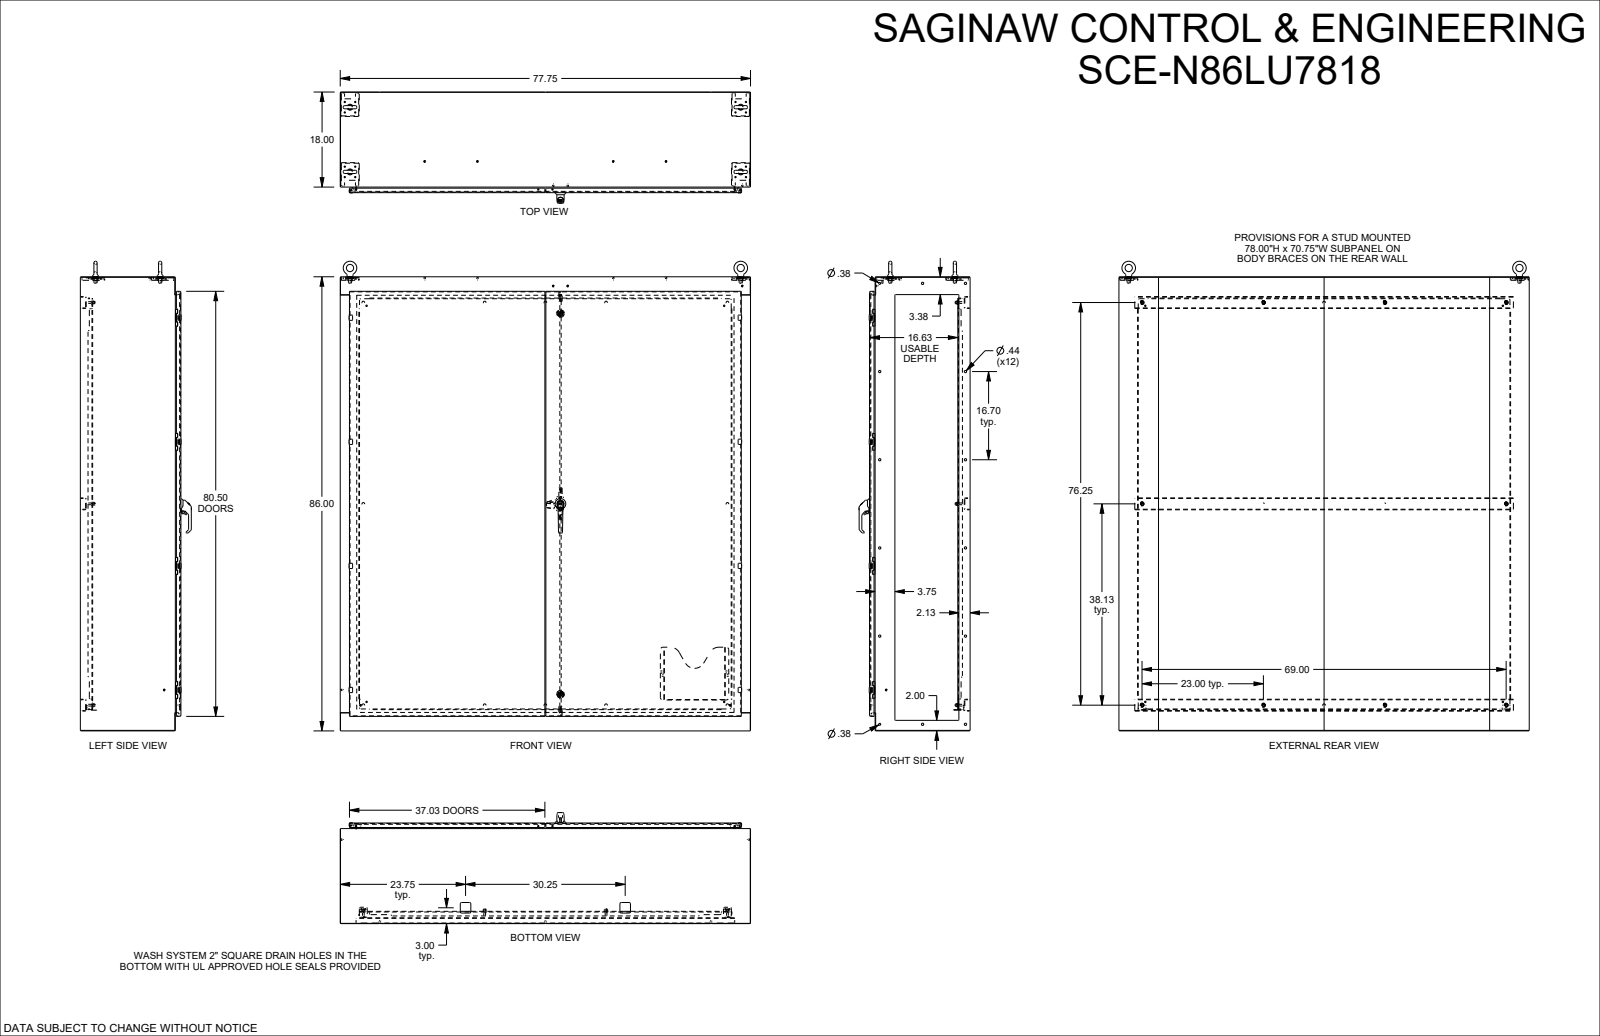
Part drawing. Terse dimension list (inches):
name: SCE-N86LU7818_REV1
written by: SolidWorks 2023 (AUTOMOTIVE_DESIGN)
unit: in
bodies: 34 solids, 5085 faces (2411 planar, 1670 cylindrical, 1004 other)
size: 88.945 × 77.75 × 21.046
volume: 2 163 in³; area: 41 492 in²
holes: 18× ⌀0.25, 18× ⌀0.375, 16× ⌀0.205, 16× ⌀0.244, 12× ⌀0.437, 8× ⌀0.04, 8× ⌀0.218, 4× ⌀0.17, 4× ⌀0.256, 4× ⌀0.875, 2× ⌀0.206, 2× ⌀0.343
bosses: 24× ⌀0.17, 16× ⌀0.25, 16× ⌀0.24, 12× ⌀0.645, 10× ⌀0.196, 4× ⌀1.173, 4× ⌀0.6, 2× ⌀1.4
rounds: 102× R0.03, 88× R0.015, 67× R0.125, 41× R0.04, 38× R0.167, 34× R0.062, 32× R0.063, 32× R0.229
face distances: 0.104, 18.954, 18.85, 19.058, 85.896, 17.896, 1.058, 86, 85.792, 77.646
hole spacings: 23.5, 1.979, 47, 72.868, 1.4, 76.525, 16.7, 23.302
